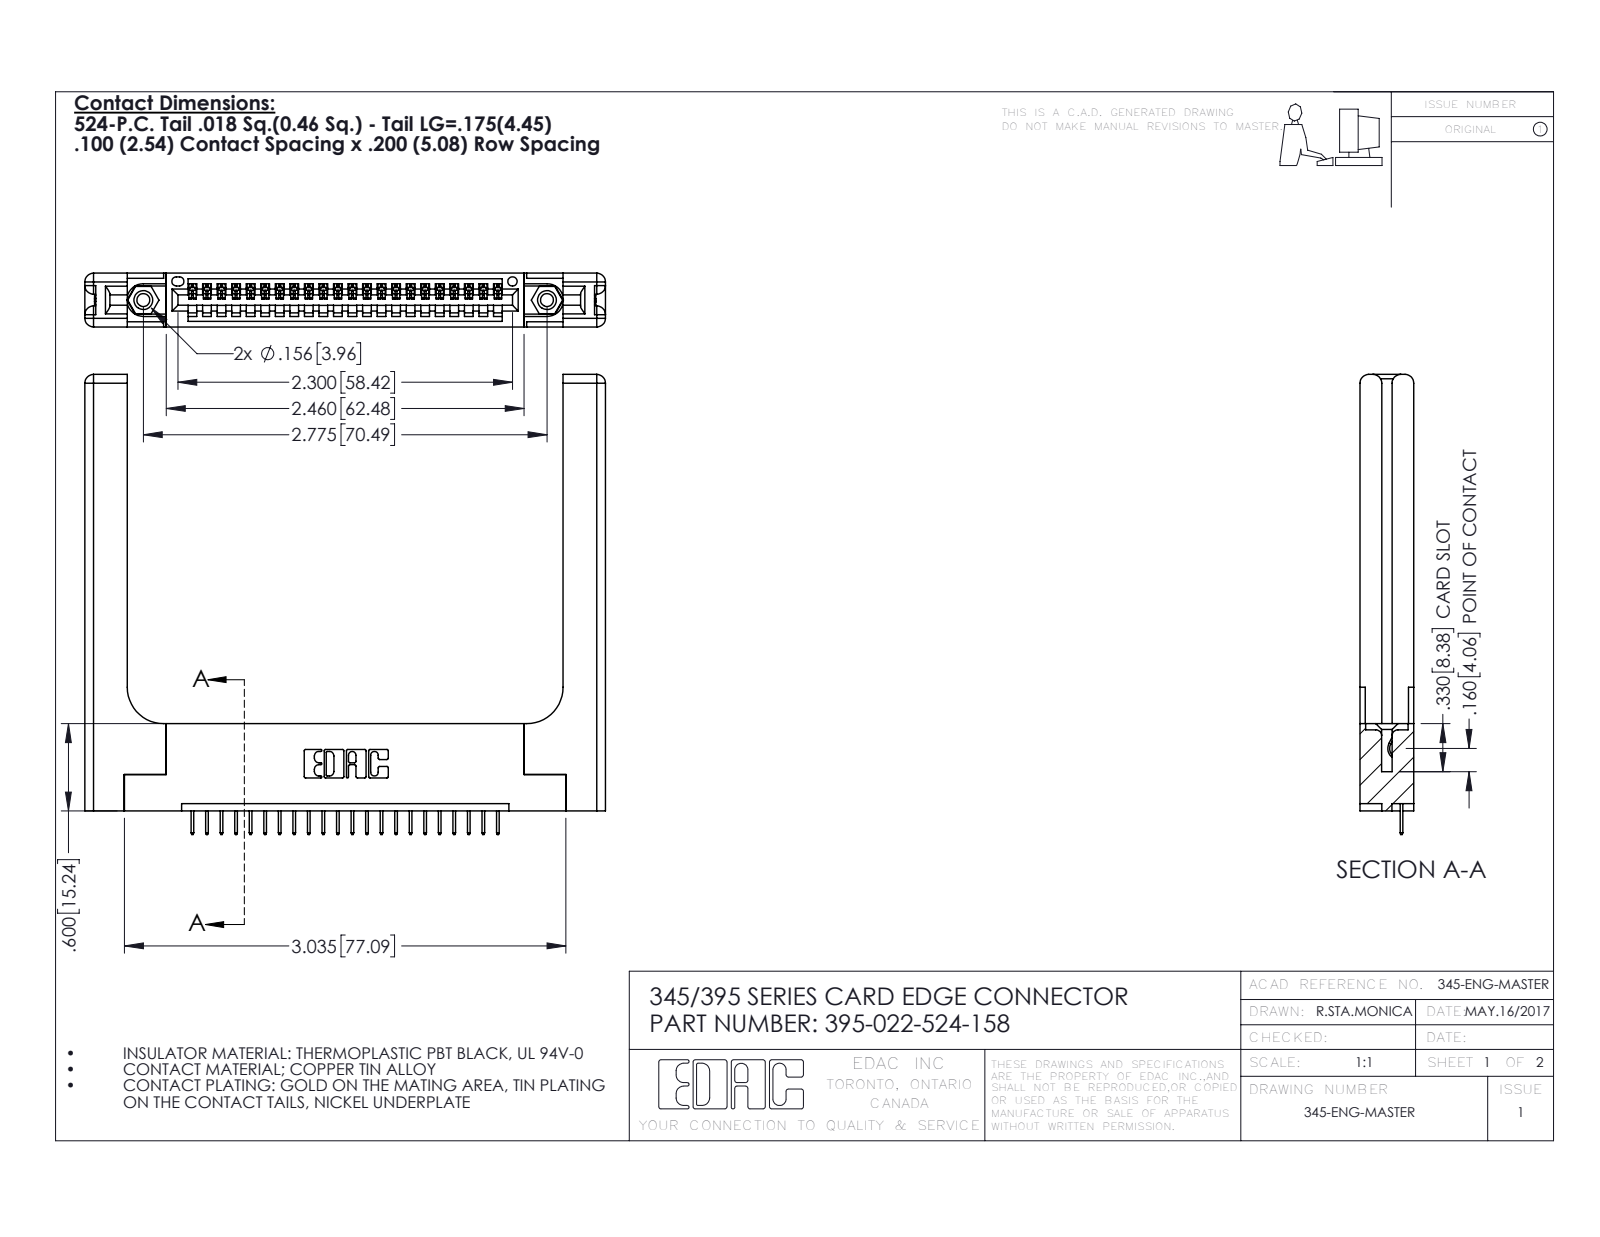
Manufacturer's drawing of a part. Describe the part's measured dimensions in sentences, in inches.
The part is named "345-292-001_345-293-124; 345-250-001_345-250-001-102; 345-220-058_345-220-058; 345 Part_Flush Mounting Lugs - 0.156 Dia-TH (+1 more)". Its 3-D file was written by "SolidWorks 2016 (CONFIG_CONTROL_DESIGN)". It is 27 solids with 1746 faces: 1240 planar, 446 cylindrical and 60 other. Overall it measures 3.579 by 3.162 by 0.37 inches. Its volume is 1.031 cubic inches and its surface area 24.64 square inches. Round holes: 2 of diameter 0.089, 2 of diameter 0.125, 2 of diameter 0.156, 1 of diameter 0.064. Round bosses or shafts: 2 of diameter 0.155. Partial cylindrical surfaces (rounded edges, fillets, slot ends): 44 of radius 0.006, 22 of radius 0.01, 16 of radius 0.06, 6 of radius 0.007, 6 of radius 0.031, 3 of radius 0.026, 2 of radius 0.03, 2 of radius 0.031. The main face-to-face distances are 0.37, 0.072, 0.298, 0.15, 0.148, 0.2, 0.077, 0.22, 0.098, 0.272. The hole center spacings are 0.27, 2.541, 2.775.
